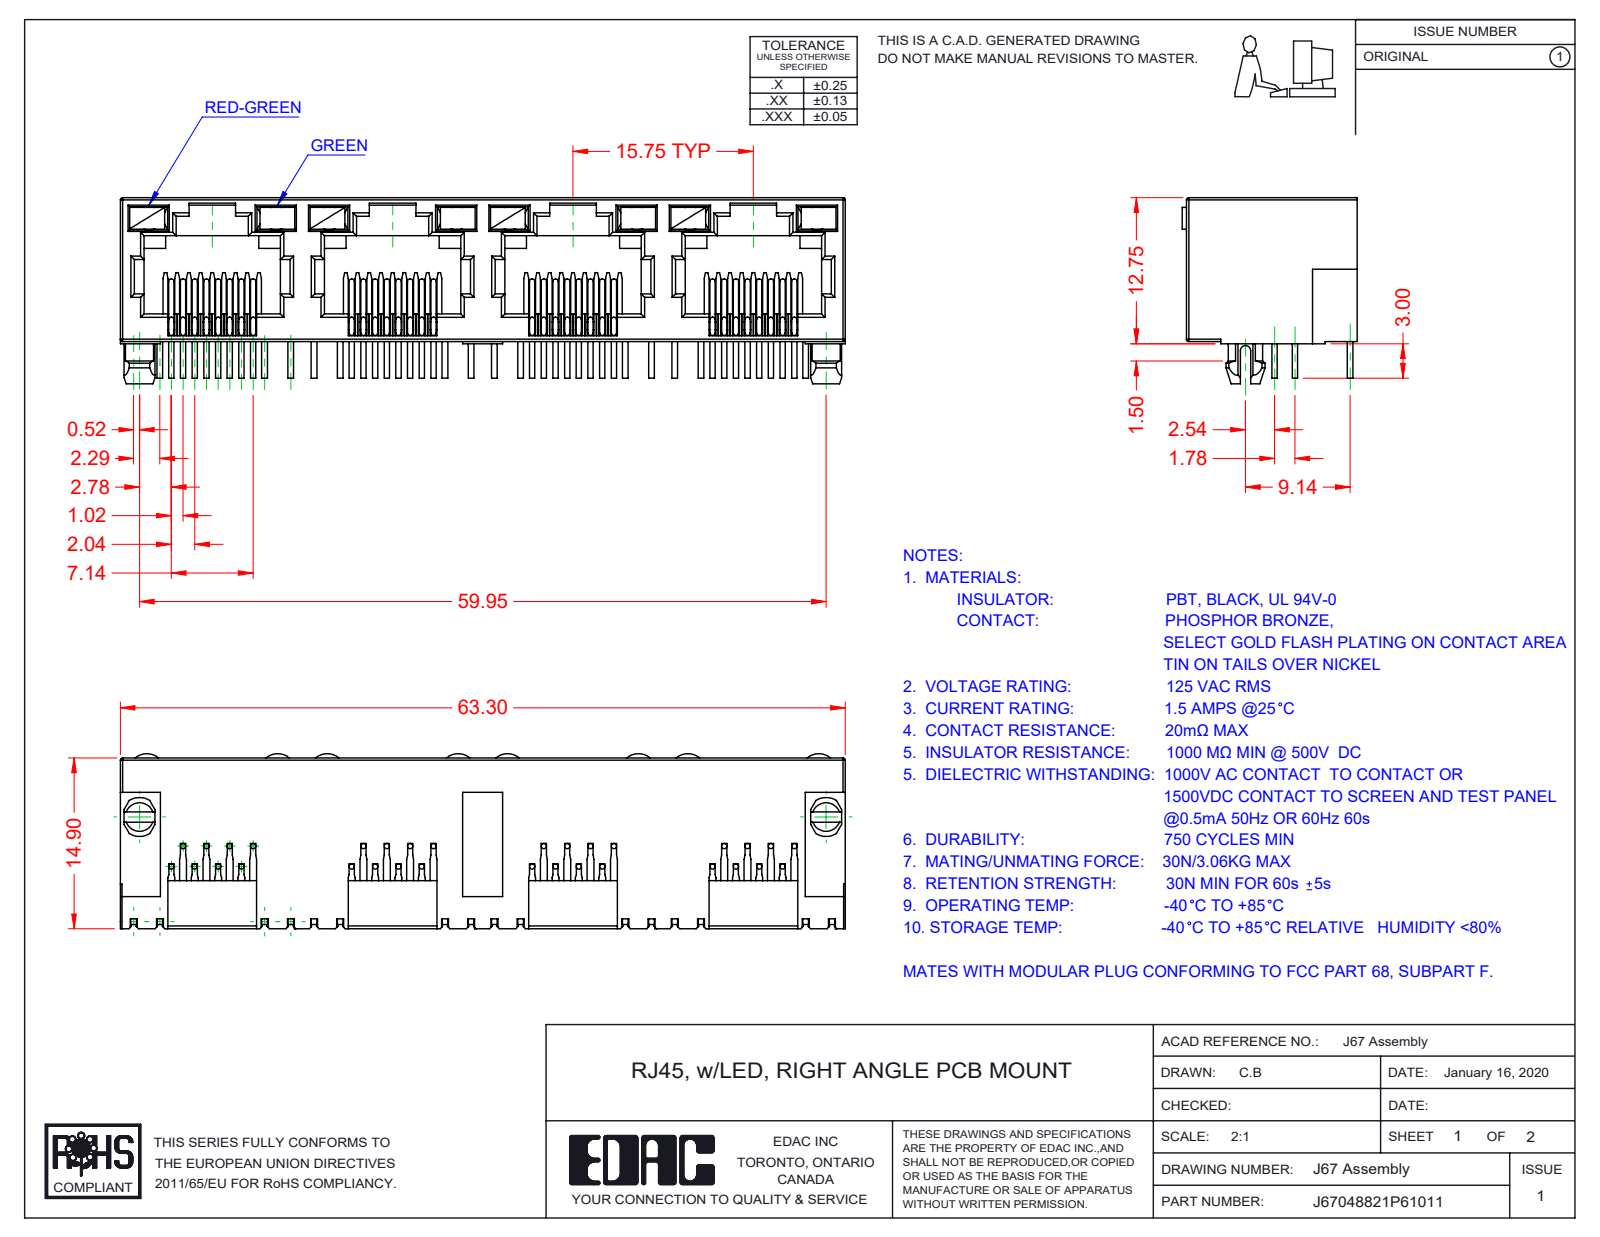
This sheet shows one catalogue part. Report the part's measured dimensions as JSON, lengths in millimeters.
{"part_name": "67 LED LH_6-Red-Green; J67048822P63011; 67 Contacts; 67 LED RH_3-Green (+1 more)", "step_written_by": "SolidWorks 2016 (CONFIG_CONTROL_DESIGN)", "units": "millimeters", "bodies": {"solids": 41, "faces": 2473, "planar": 1781, "cylindrical": 484, "other": 208}, "overall_size": [63.3, 16.25, 15.28], "volume_mm3": 5159, "surface_area_mm2": 11573, "round_bosses_or_shafts": [[0.46, 96]], "partial_cylinders_radius": [[0.2, 66], [0.3, 29], [0.45, 9], [1.55, 8], [1.5, 2], [1.7, 2], [0.35, 1], [1, 1]], "face_to_face_distances": [0.5, 12.55, 1.89, 0.89, 10, 15.75, 1, 1.39, 11, 11.89]}
